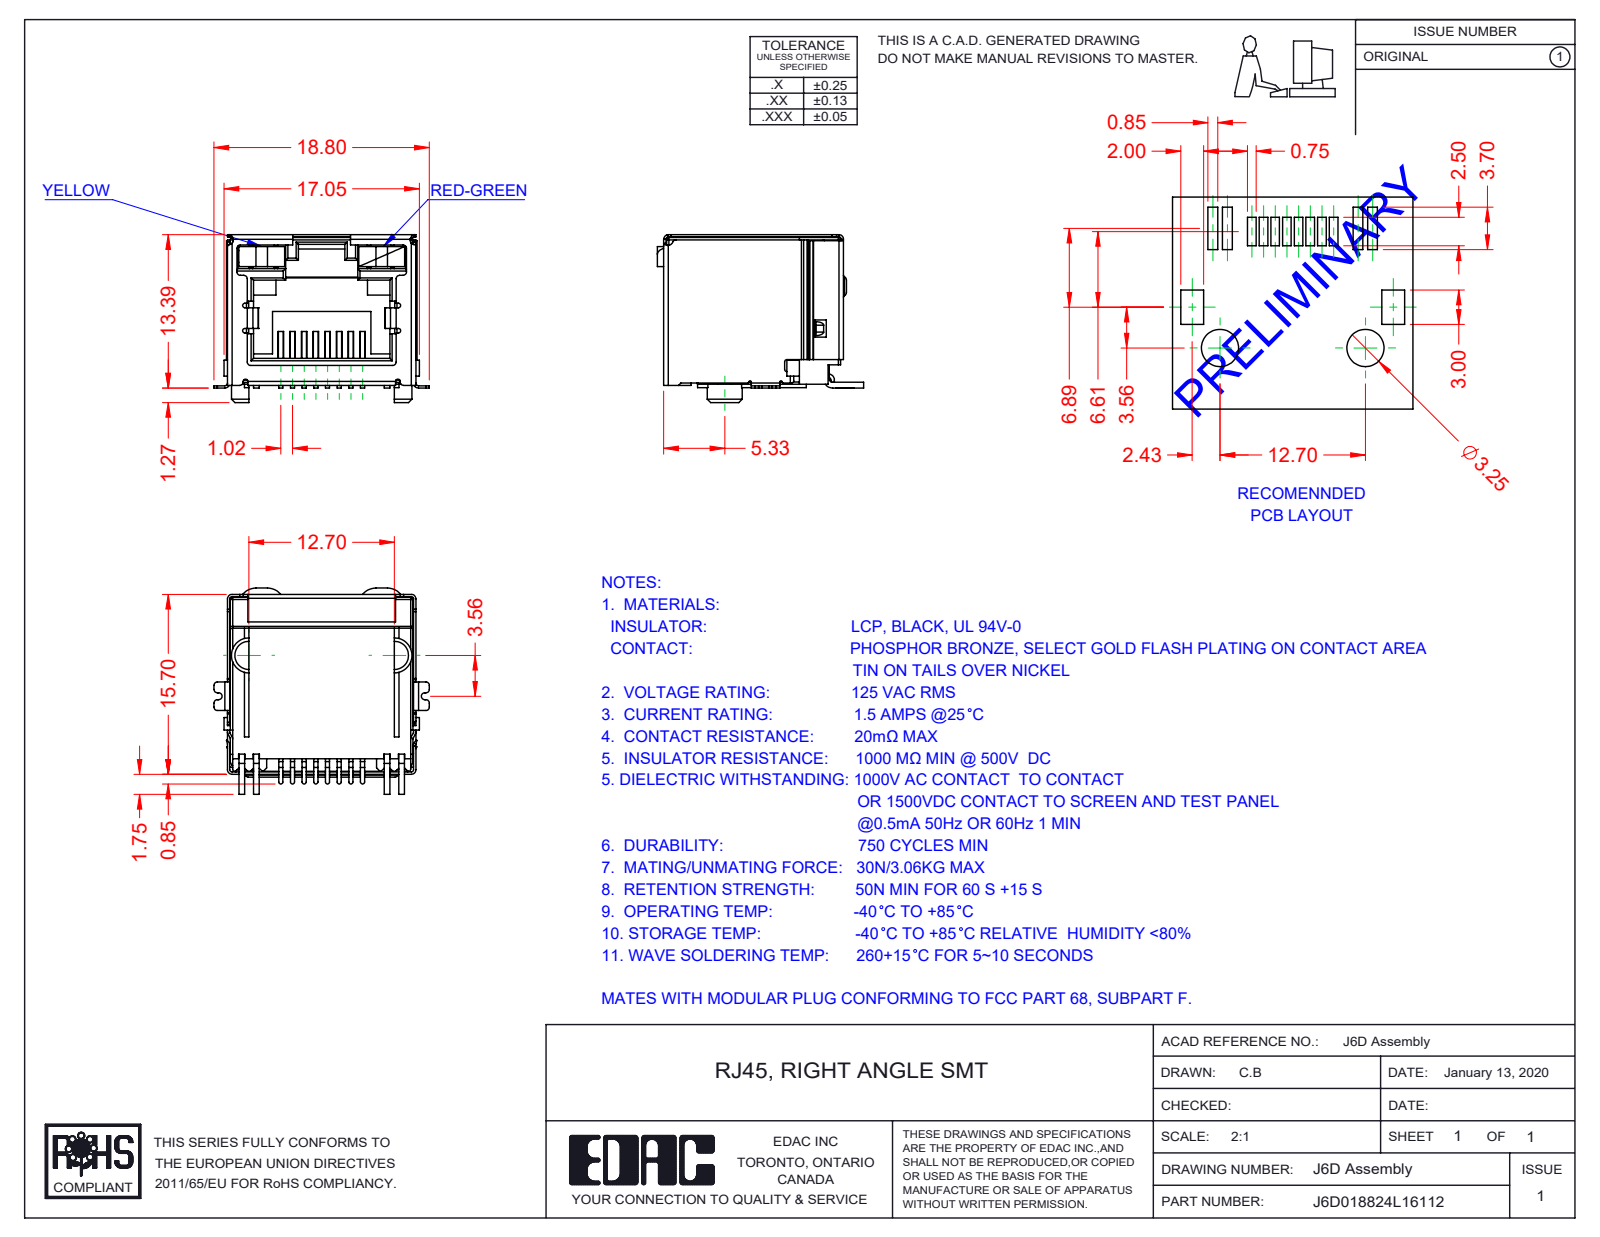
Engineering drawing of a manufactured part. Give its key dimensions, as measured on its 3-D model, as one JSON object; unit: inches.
{"part_name": "6D Insulator; J6D018824L16112; 6D LED LH_1-Yellow; 6D Shield_LED - No EMI (+2 more)", "step_written_by": "SolidWorks 2016 (CONFIG_CONTROL_DESIGN)", "units": "inches", "bodies": {"solids": 12, "faces": 896, "planar": 645, "cylindrical": 218, "other": 33}, "overall_size": [0.74, 0.709, 0.577], "volume_in3": 0.11, "surface_area_in2": 7.592, "partial_cylinders_radius": [[0.012, 39], [0.008, 37], [0.016, 16], [0.004, 12], [0.006, 8], [0.007, 8], [0.02, 6], [0.059, 5]], "face_to_face_distances": [0.63, 0.64, 0.638, 0.089, 0.039, 0.628, 0.632, 0.504, 0.018, 0.648]}
